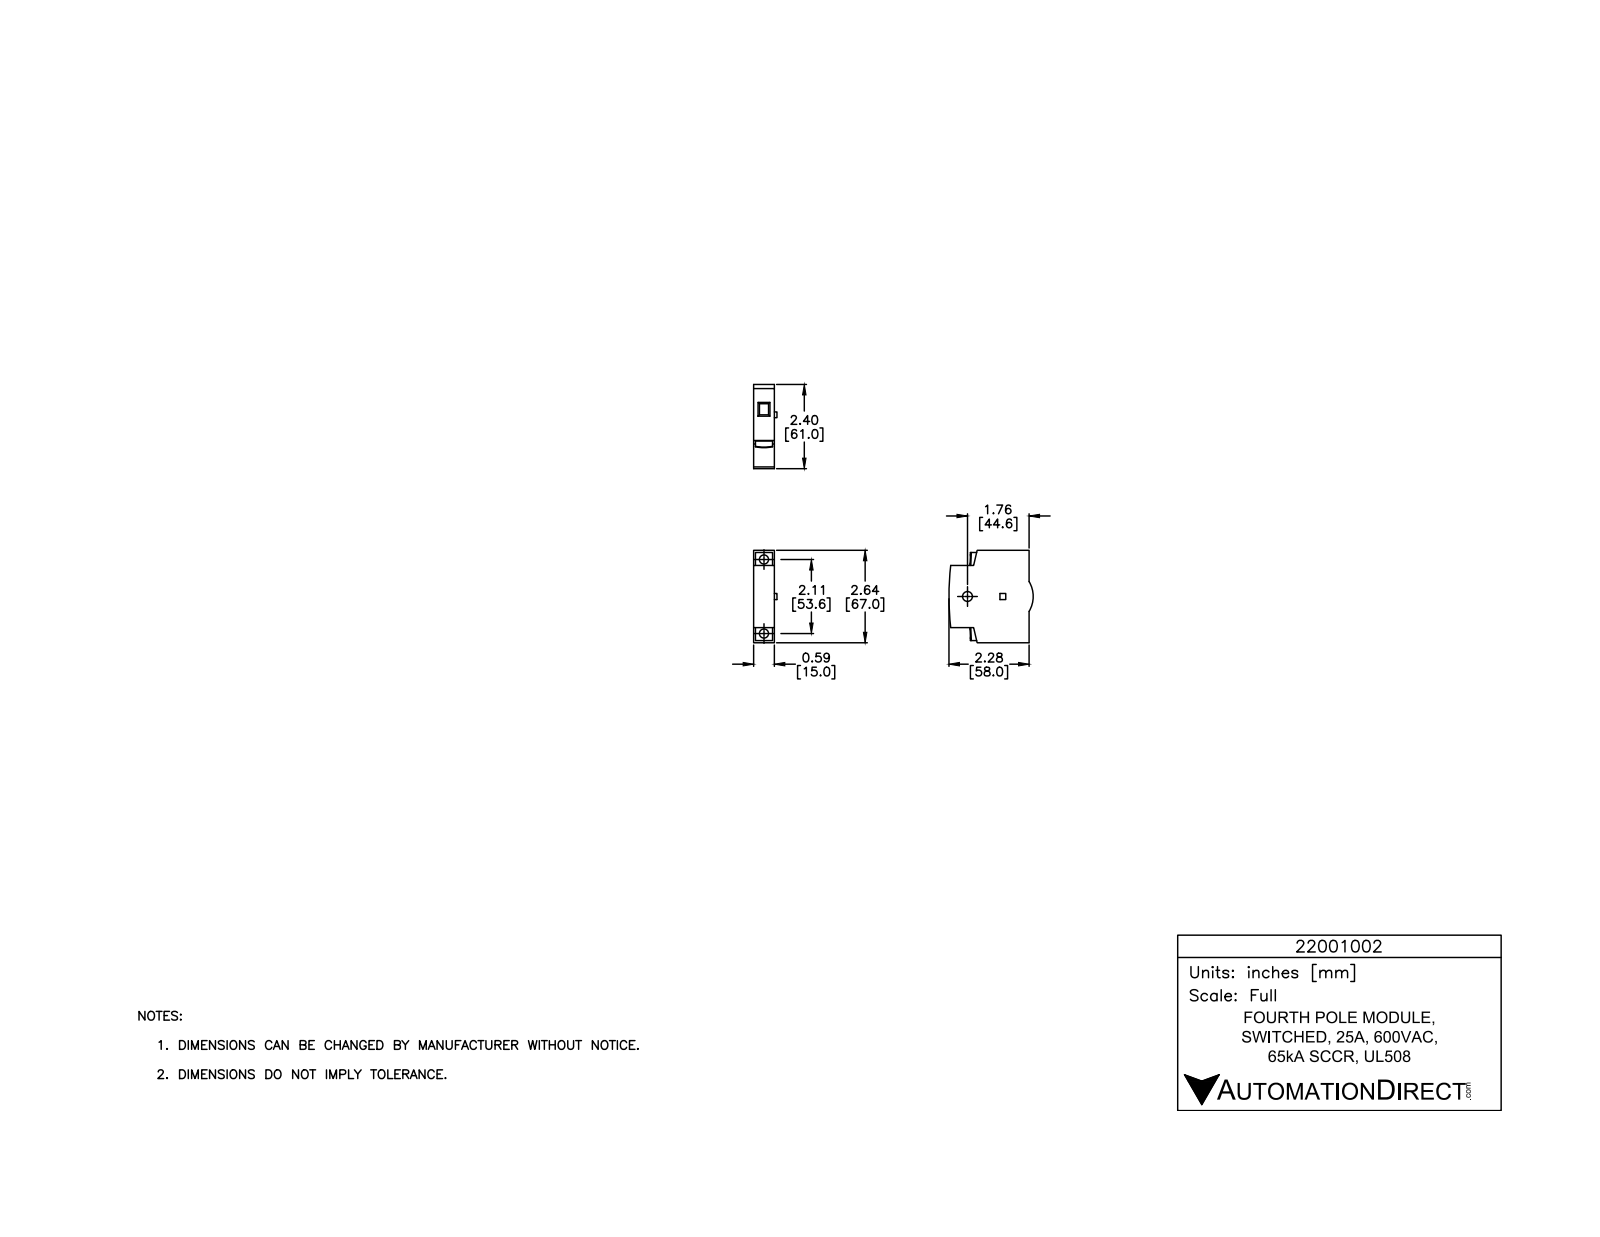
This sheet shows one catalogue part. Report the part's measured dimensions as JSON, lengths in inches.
{"part_name": "22001002-UL", "step_written_by": "SolidWorks 2021 (CONFIG_CONTROL_DESIGN)", "units": "inches", "bodies": {"solids": 1, "faces": 61, "planar": 46, "cylindrical": 11, "other": 4}, "overall_size": [2.638, 2.402, 0.665], "volume_in3": 3.141, "surface_area_in2": 18.13, "round_holes": [[0.26, 2], [0.283, 1]], "partial_cylinders_radius": [[0.827, 1], [7.874, 1]], "face_to_face_distances": [0.591, 2.638, 0.433, 2.205, 1.772, 0.063, 2.575, 0.37, 2.142, 0.051], "hole_center_spacings": [2.11]}
